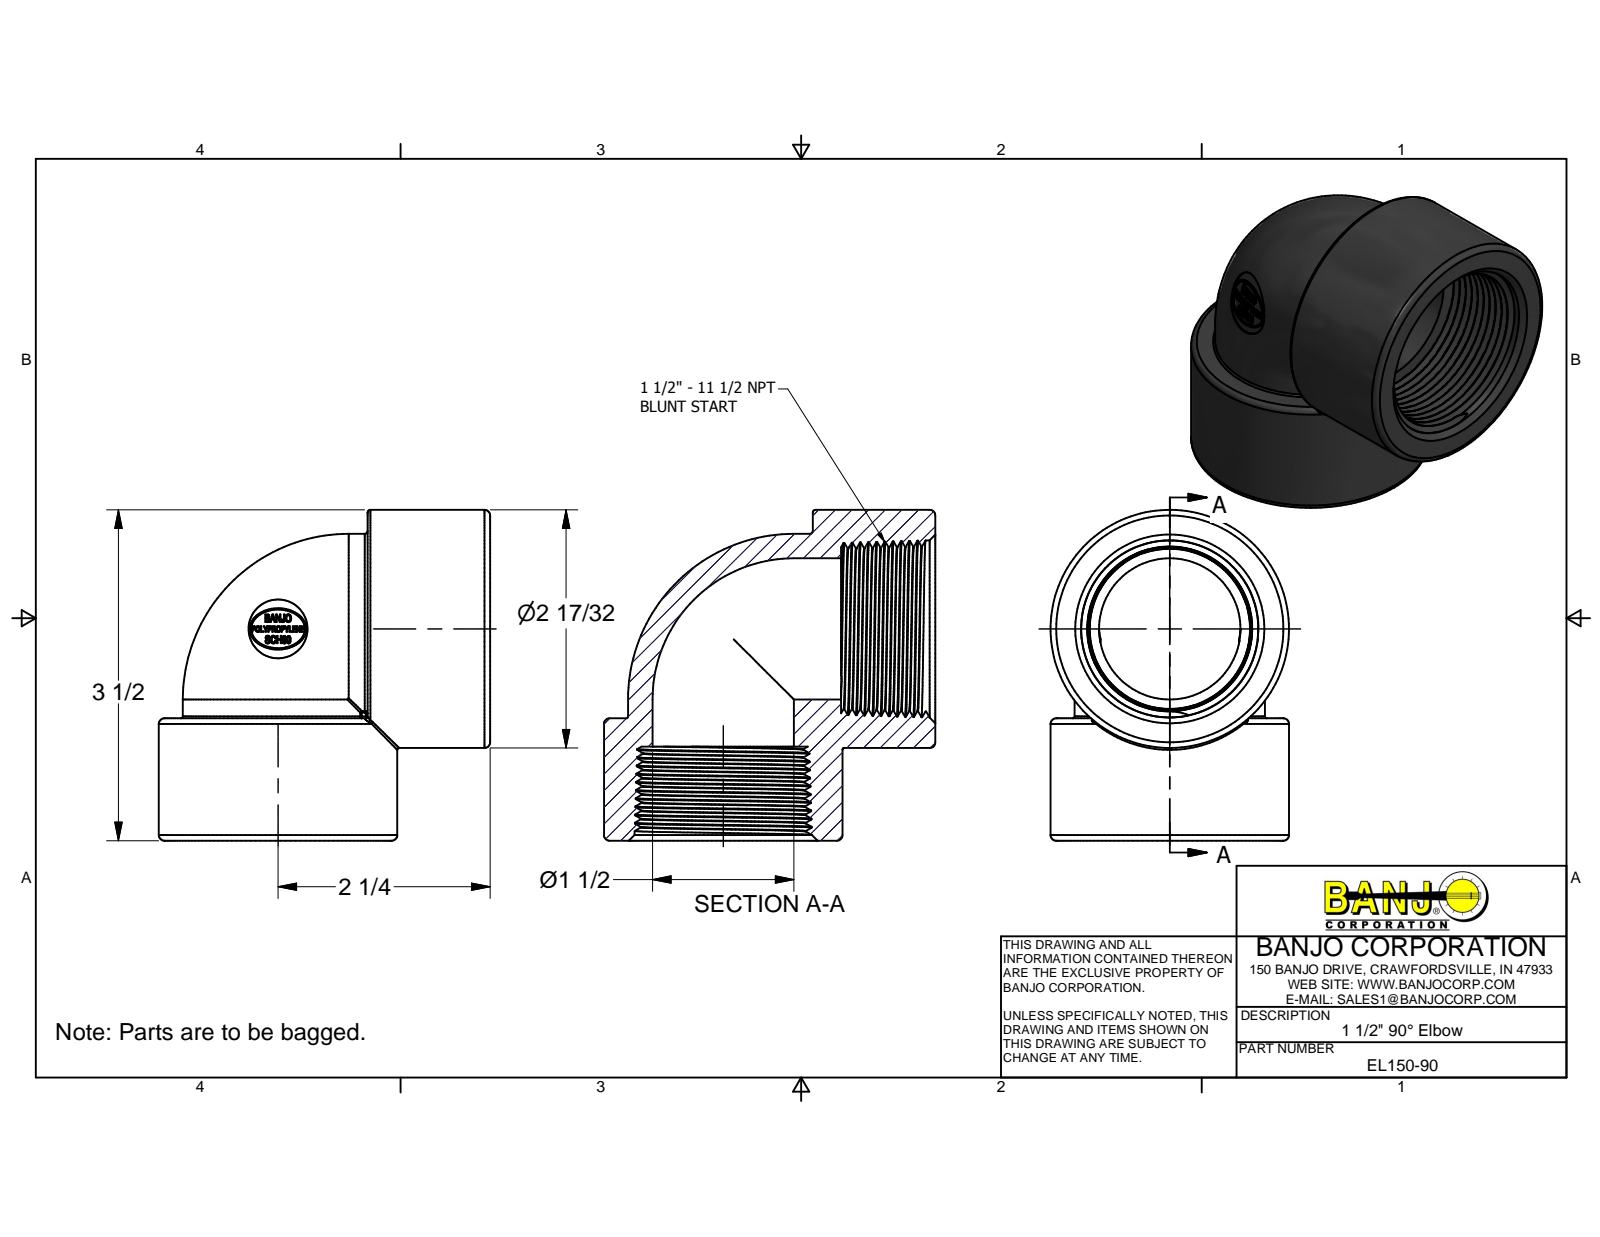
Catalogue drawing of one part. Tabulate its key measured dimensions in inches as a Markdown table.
| quantity | value |
| --- | --- |
| part name | EL150-90; EL150-90U |
| STEP written by | Autodesk Inventor 2022 (AUTOMOTIVE_DESIGN) |
| units | inches |
| bodies | 1 solid, 418 faces (160 planar, 19 cylindrical, 239 other) |
| overall size | 3.515 × 3.515 × 2.53 |
| volume | 9.063 in³ |
| surface area | 67.68 in² |
| round holes (diameter × count) | 1.5 × 2, 0.625 × 1 |
| round bosses / shafts (diameter × count) | 2.53 × 2, 2.02 × 2 |
| partial cylindrical surfaces (radius × count) | 0.02 × 9, 0.535 × 2 |
| main face-to-face distances | 1.3, 1, 0.3, 2.279, 1.279, 0.979, 0.04, 2.272, 1.272, 0.972 |
